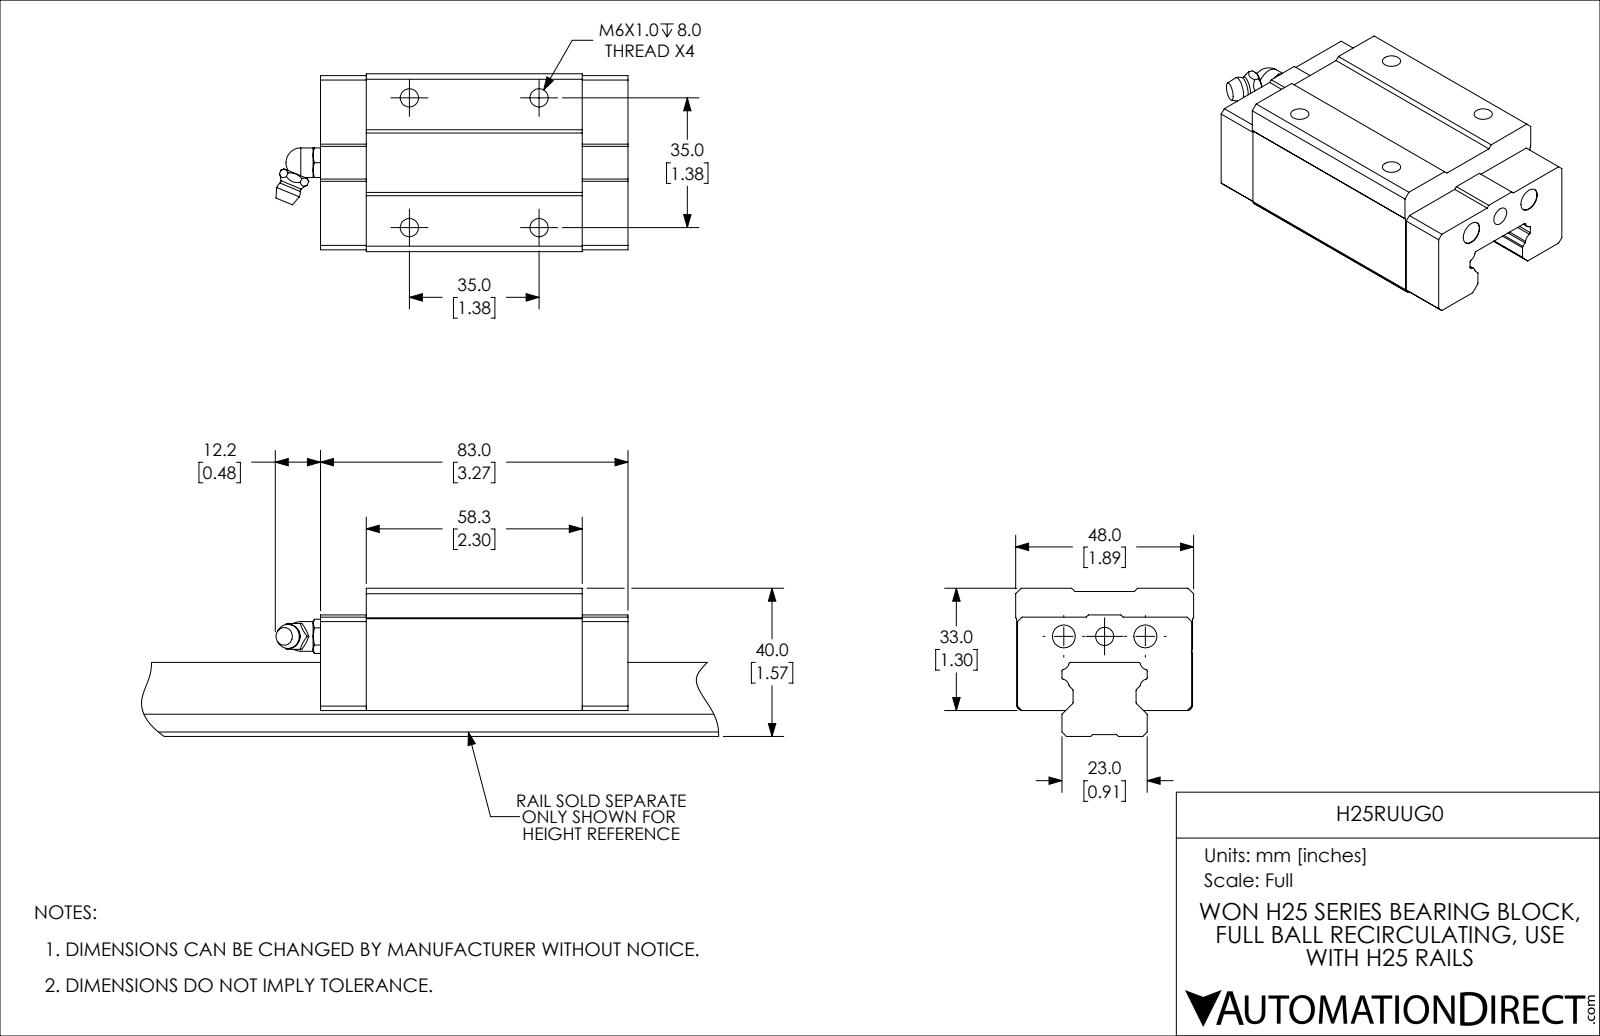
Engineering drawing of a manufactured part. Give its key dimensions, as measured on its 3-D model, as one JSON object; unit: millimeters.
{"part_name": "H25RUUG0", "step_written_by": "SolidWorks 2019 (CONFIG_CONTROL_DESIGN)", "units": "millimeters", "bodies": {"solids": 2, "faces": 150, "planar": 75, "cylindrical": 45, "other": 30}, "overall_size": [95, 48, 33], "volume_mm3": 98776, "surface_area_mm2": 19171, "round_holes": [[4.92, 3], [4.92, 2], [6.2, 2]], "round_bosses_or_shafts": [[8, 1], [6, 1]], "partial_cylinders_radius": [[1, 5], [0.4, 4], [0.5, 4], [0.8, 4], [2, 4]], "face_to_face_distances": [47.5, 20, 13, 33, 47.25, 32.1, 19.1, 0.9, 83, 25.2], "hole_center_spacings": [35, 11, 49.5, 22]}
